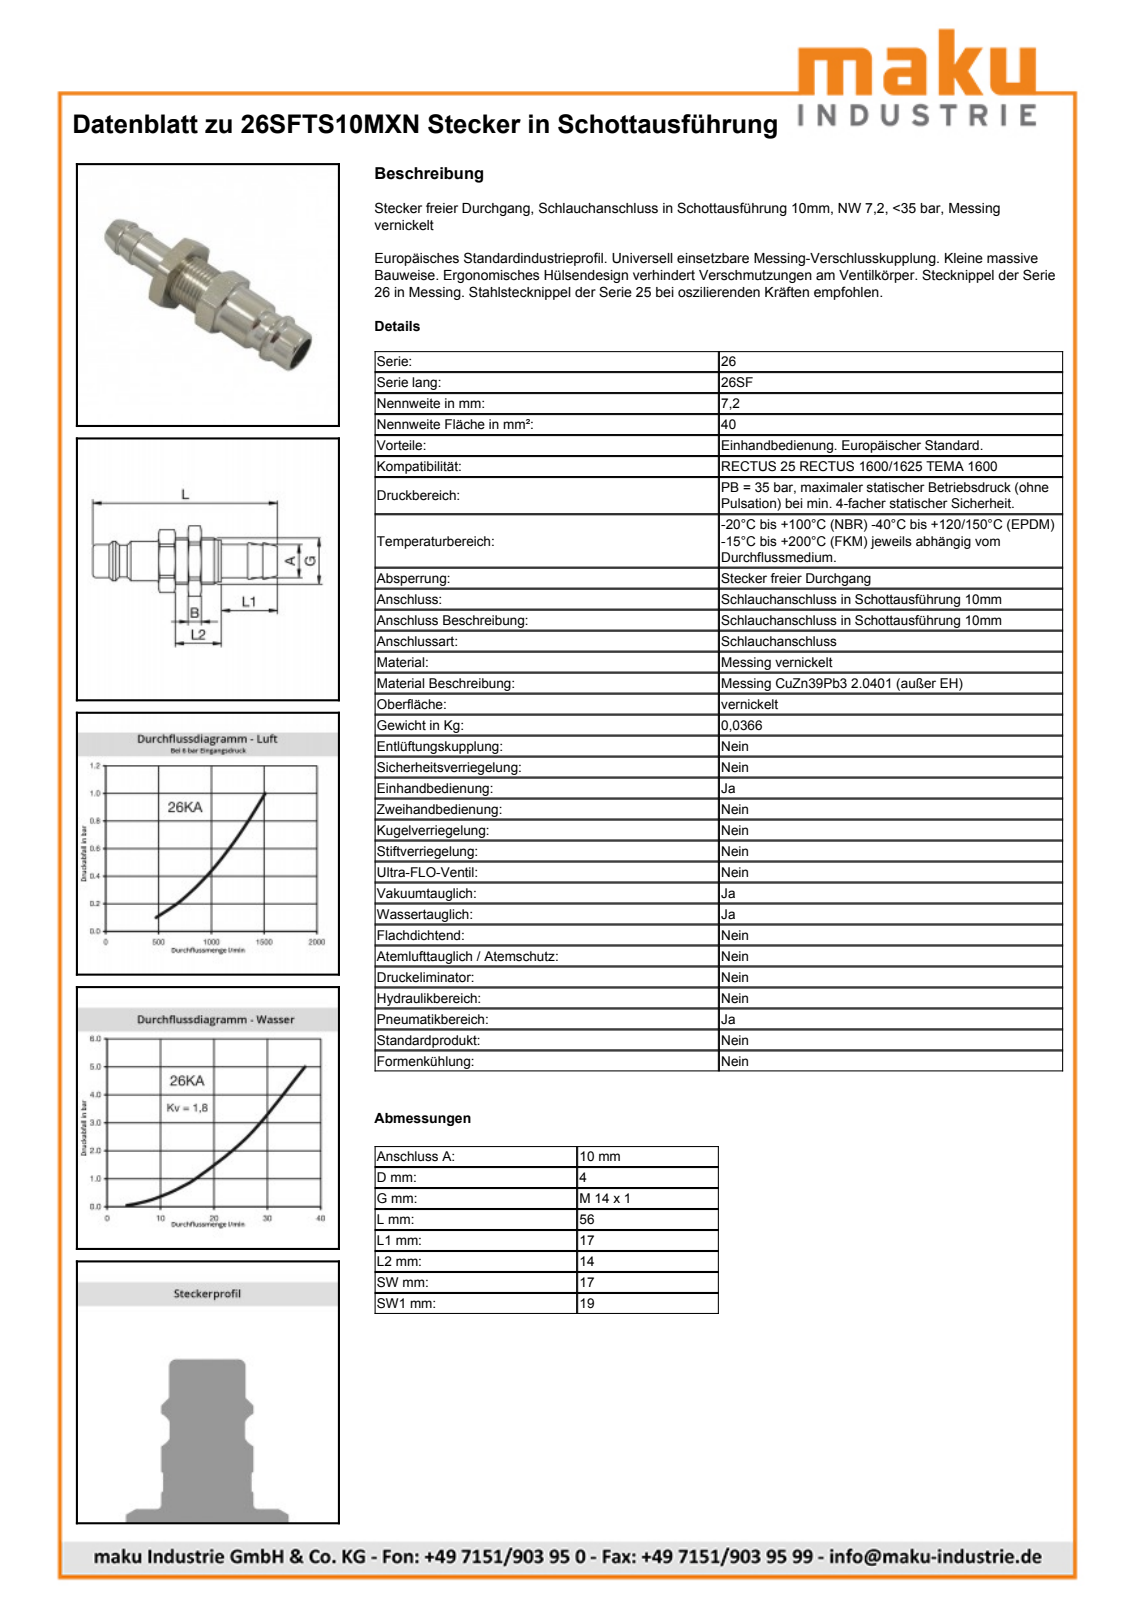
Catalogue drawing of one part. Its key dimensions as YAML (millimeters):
part_name: "D105668; D105667; D105666"
step_written_by: "Autodesk Inventor 2011 (AUTOMOTIVE_DESIGN)"
units: millimeters
bodies: {solids: 2, faces: 80, planar: 21, cylindrical: 21, other: 38}
overall_size: [56, 21.38, 19.8]
volume: 4594
surface_area: 4593
round_holes:
  - {diameter: 7.8, count: 1}
  - {diameter: 14, count: 1}
round_bosses_or_shafts:
  - {diameter: 12.6, count: 1}
  - {diameter: 12, count: 1}
  - {diameter: 10, count: 1}
  - {diameter: 9.75, count: 1}
partial_cylinders:
  - {radius: 9.57, count: 1}
  - {radius: 10.7, count: 1}
face_to_face_distances: [19, 17, 4, 9.2, 13.2, 5, 4.2, 8.2, 14, 9.8]
